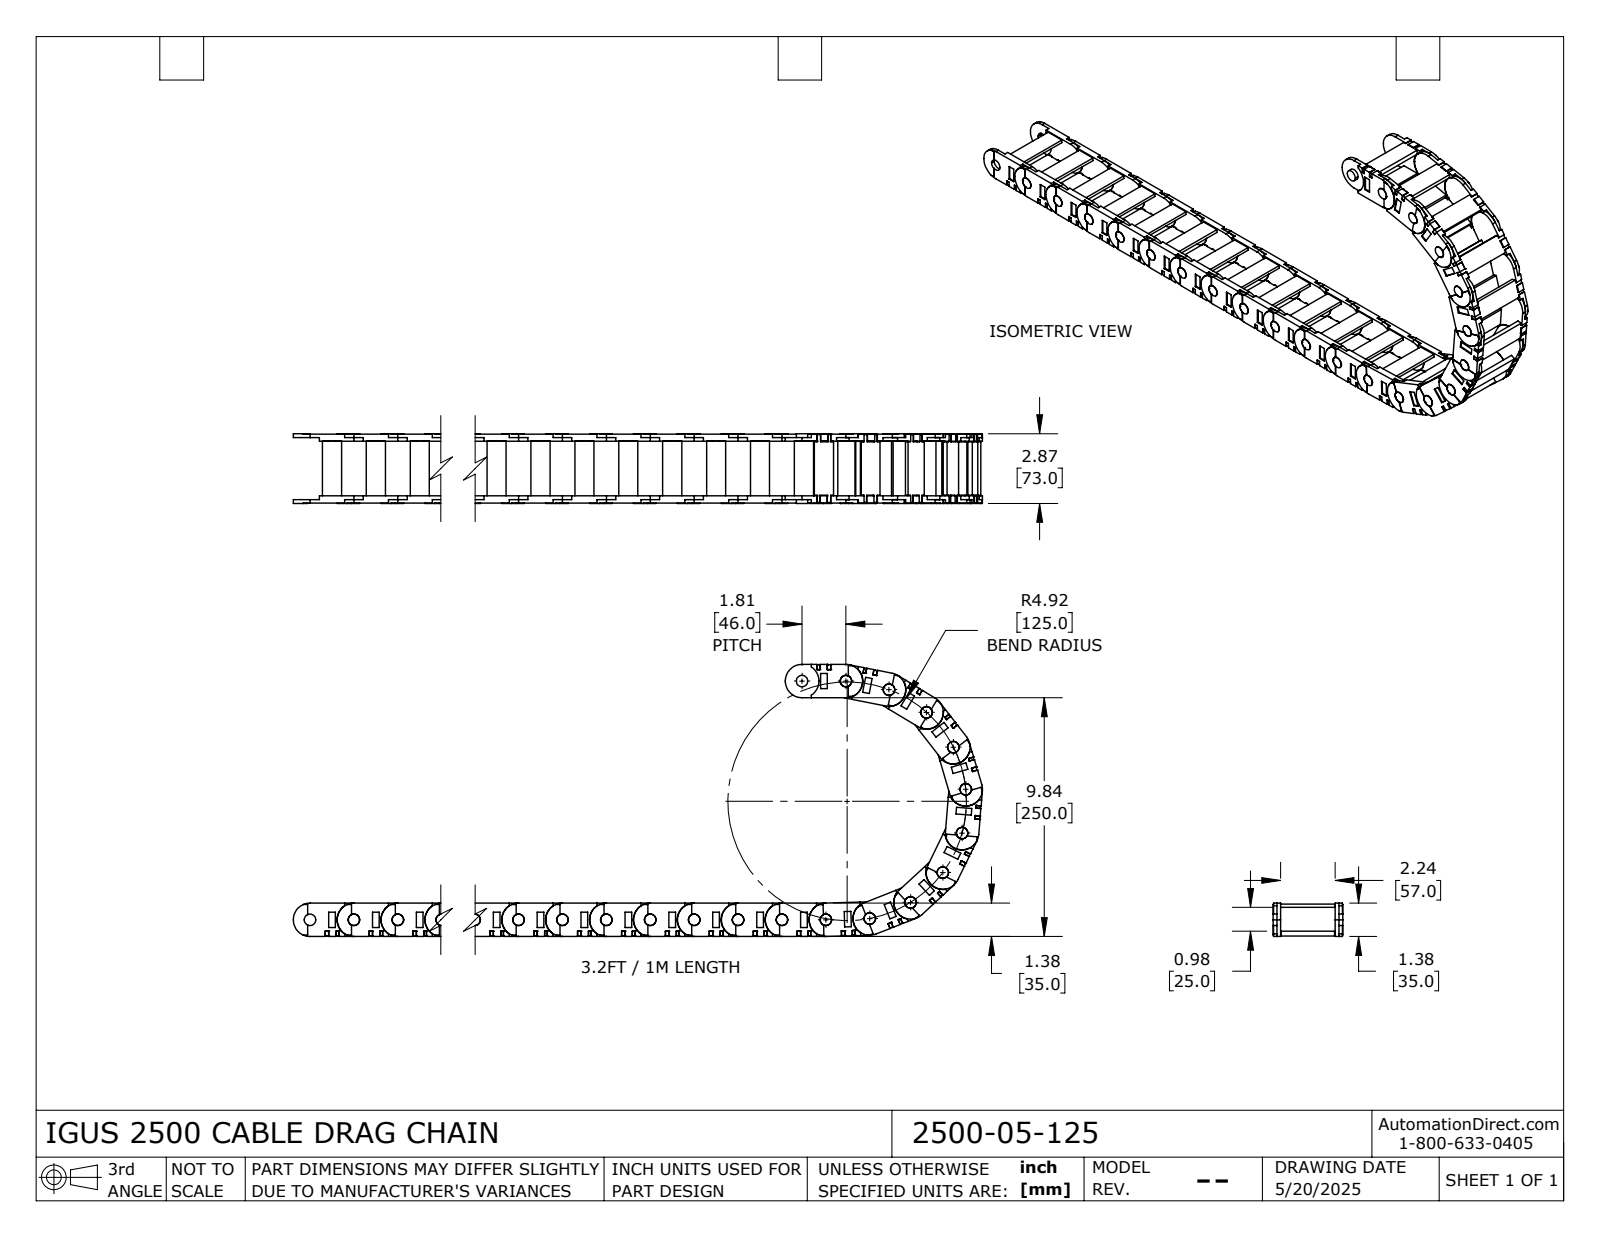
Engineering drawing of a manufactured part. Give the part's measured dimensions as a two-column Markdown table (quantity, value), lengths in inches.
| quantity | value |
| --- | --- |
| part name | 2500_05_125 |
| STEP written by | SolidWorks 2024 (AUTOMOTIVE_DESIGN) |
| units | inches |
| bodies | 66 solids, 2398 faces (1870 planar, 528 cylindrical, 0 other) |
| overall size | 28.879 × 11.22 × 2.874 |
| volume | 45.18 in³ |
| surface area | 663.9 in² |
| round holes (diameter × count) | 0.473 × 22 |
| round bosses / shafts (diameter × count) | 0.472 × 22, 1.378 × 21 |
| partial cylindrical surfaces (radius × count) | 0.697 × 23, 0.689 × 2 |
| main face-to-face distances | 0.157, 2.402, 2.559, 0.142, 0.299, 2.543, 2.701, 2.244, 0.197, 0.134 |
| hole center spacings | 1.811, 3.622, 5.433, 7.244, 9.055, 10.866, 12.677, 3.56 |
